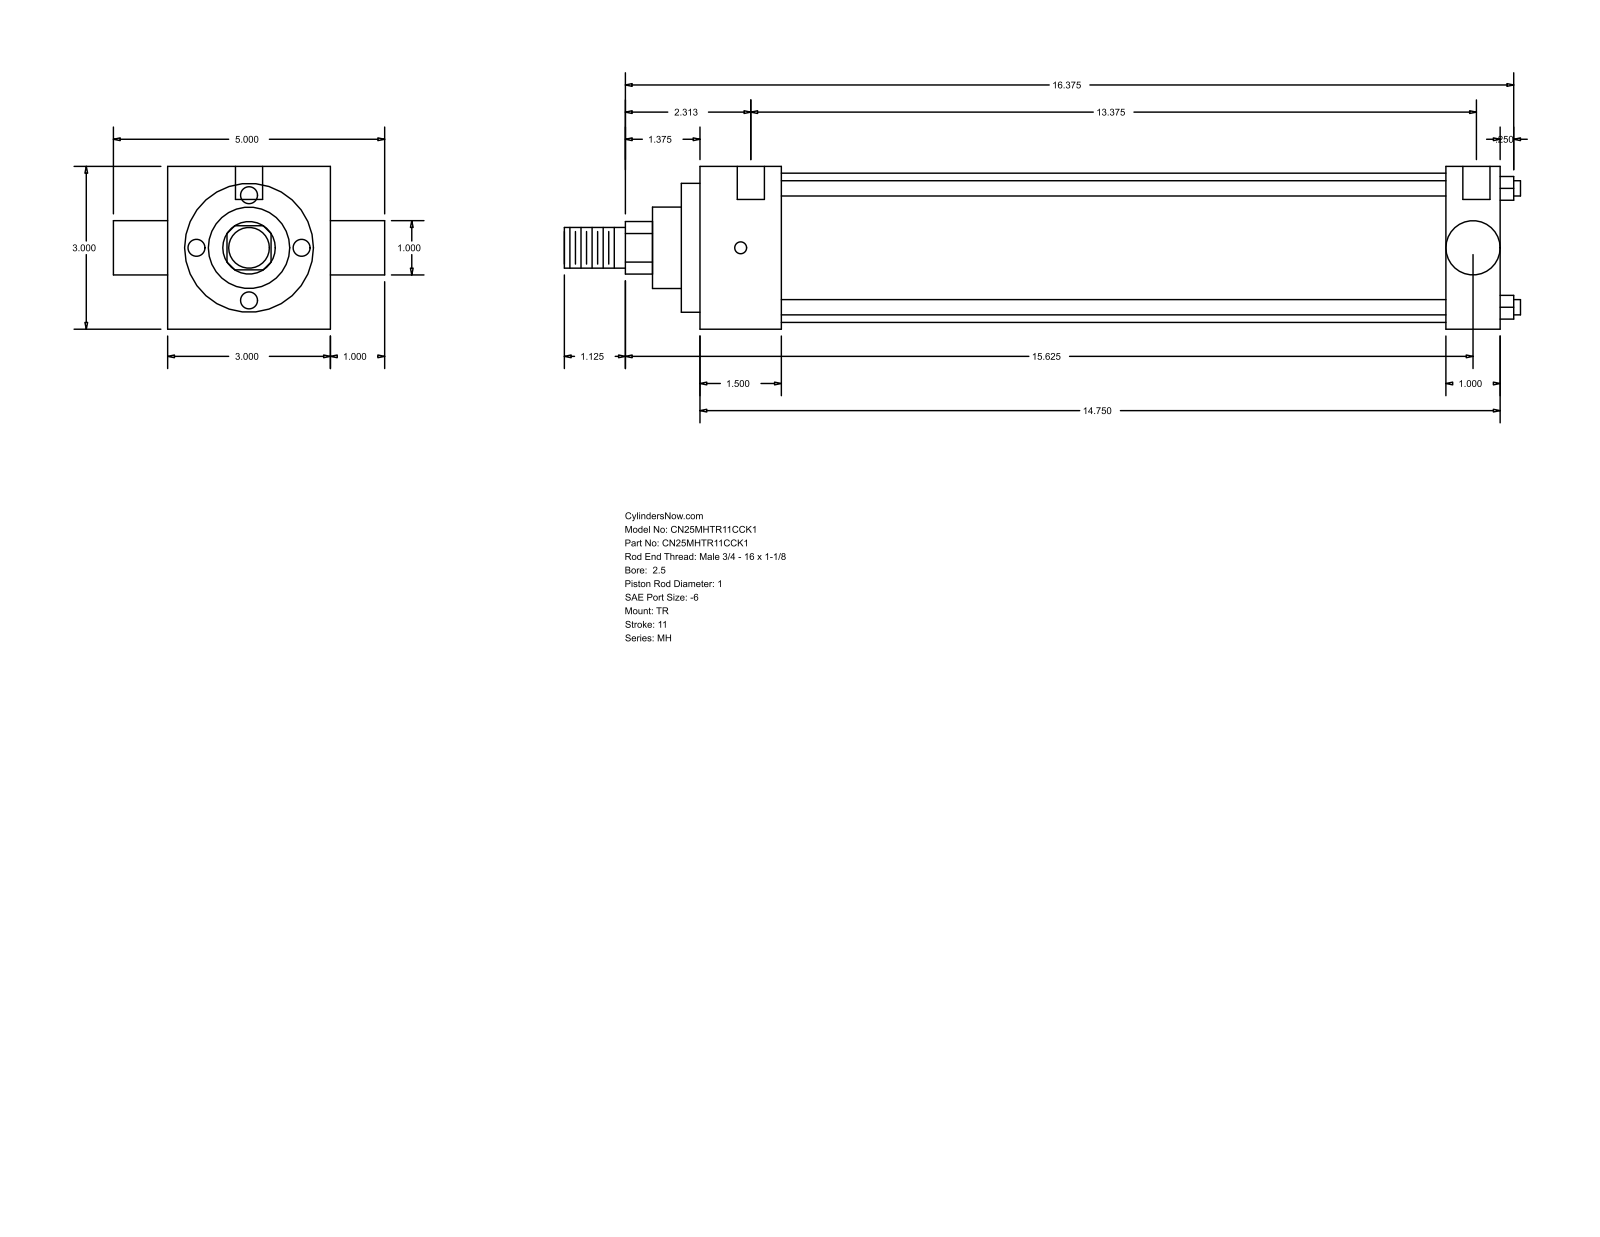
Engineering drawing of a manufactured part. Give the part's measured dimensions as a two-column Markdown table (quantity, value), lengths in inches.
| quantity | value |
| --- | --- |
| part name | MH_TR__0250_1 |
| STEP written by | GSSL Pune (CONFIG_CONTROL_DESIGN) |
| units | inches |
| bodies | 0 solids, 86 faces (61 planar, 25 cylindrical, 0 other) |
| overall size | 17.625 × 5 × 3 |
| round holes (diameter × count) | 0.219 × 3, 0.5 × 2 |
| round bosses / shafts (diameter × count) | 0.281 × 4, 2.75 × 1, 2.375 × 1, 1.5 × 1, 1 × 1, 0.998 × 1, 0.75 × 1 |
| partial cylindrical surfaces (radius × count) | 0.484 × 1 |
| main face-to-face distances | 3, 14.75, 1, 1.5, 13.25, 13.75, 12.25, 0.344, 1.844, 14.094 |
| hole center spacings | 0.125, 0.187, 13.375, 13.5, 13.562, 13.687 |
